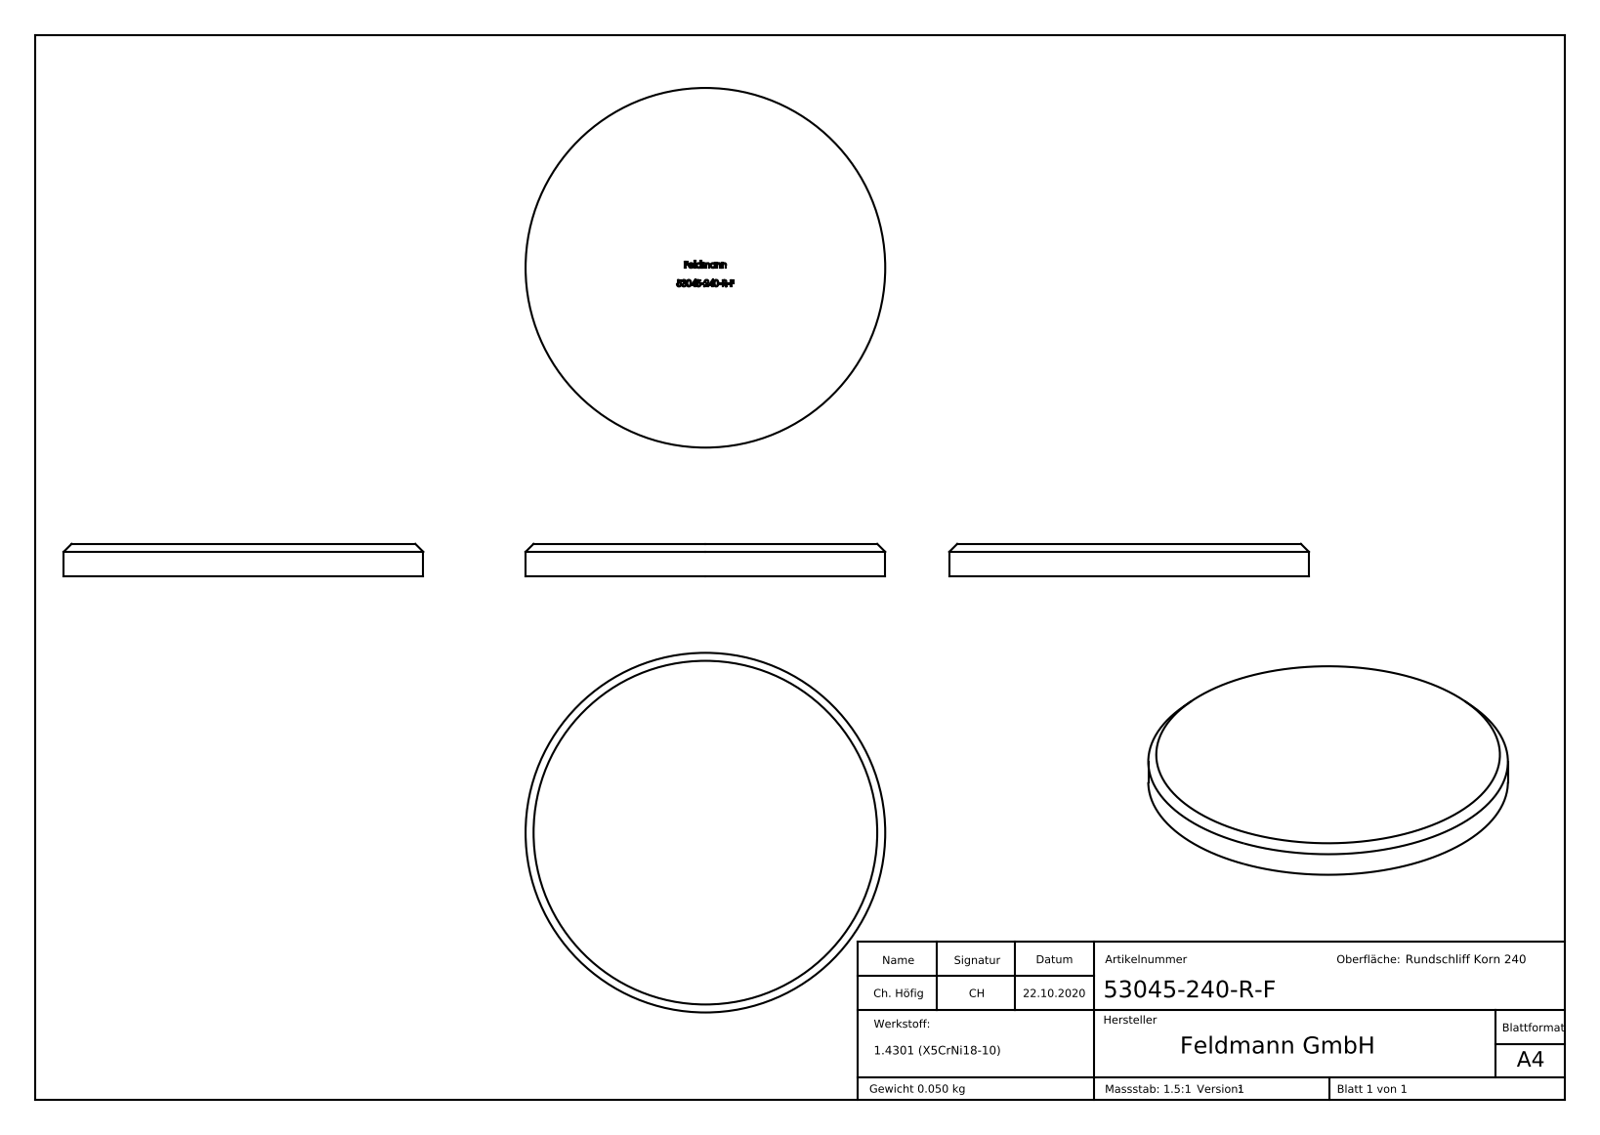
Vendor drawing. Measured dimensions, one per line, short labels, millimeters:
name: 53045-240-R-F
written by: SolidWorks 2018 (CONFIG_CONTROL_DESIGN)
unit: mm
bodies: 1 solid, 276 faces (165 planar, 2 cylindrical, 109 other)
size: 45 × 45 × 4
volume: 6 292 mm³; area: 3 669 mm²
bosses: 1× ⌀45
face distances: 4, 3.9, 2.32, 1.21, 2.2, 0.79, 3.49, 0.53, 0.45, 1.29
